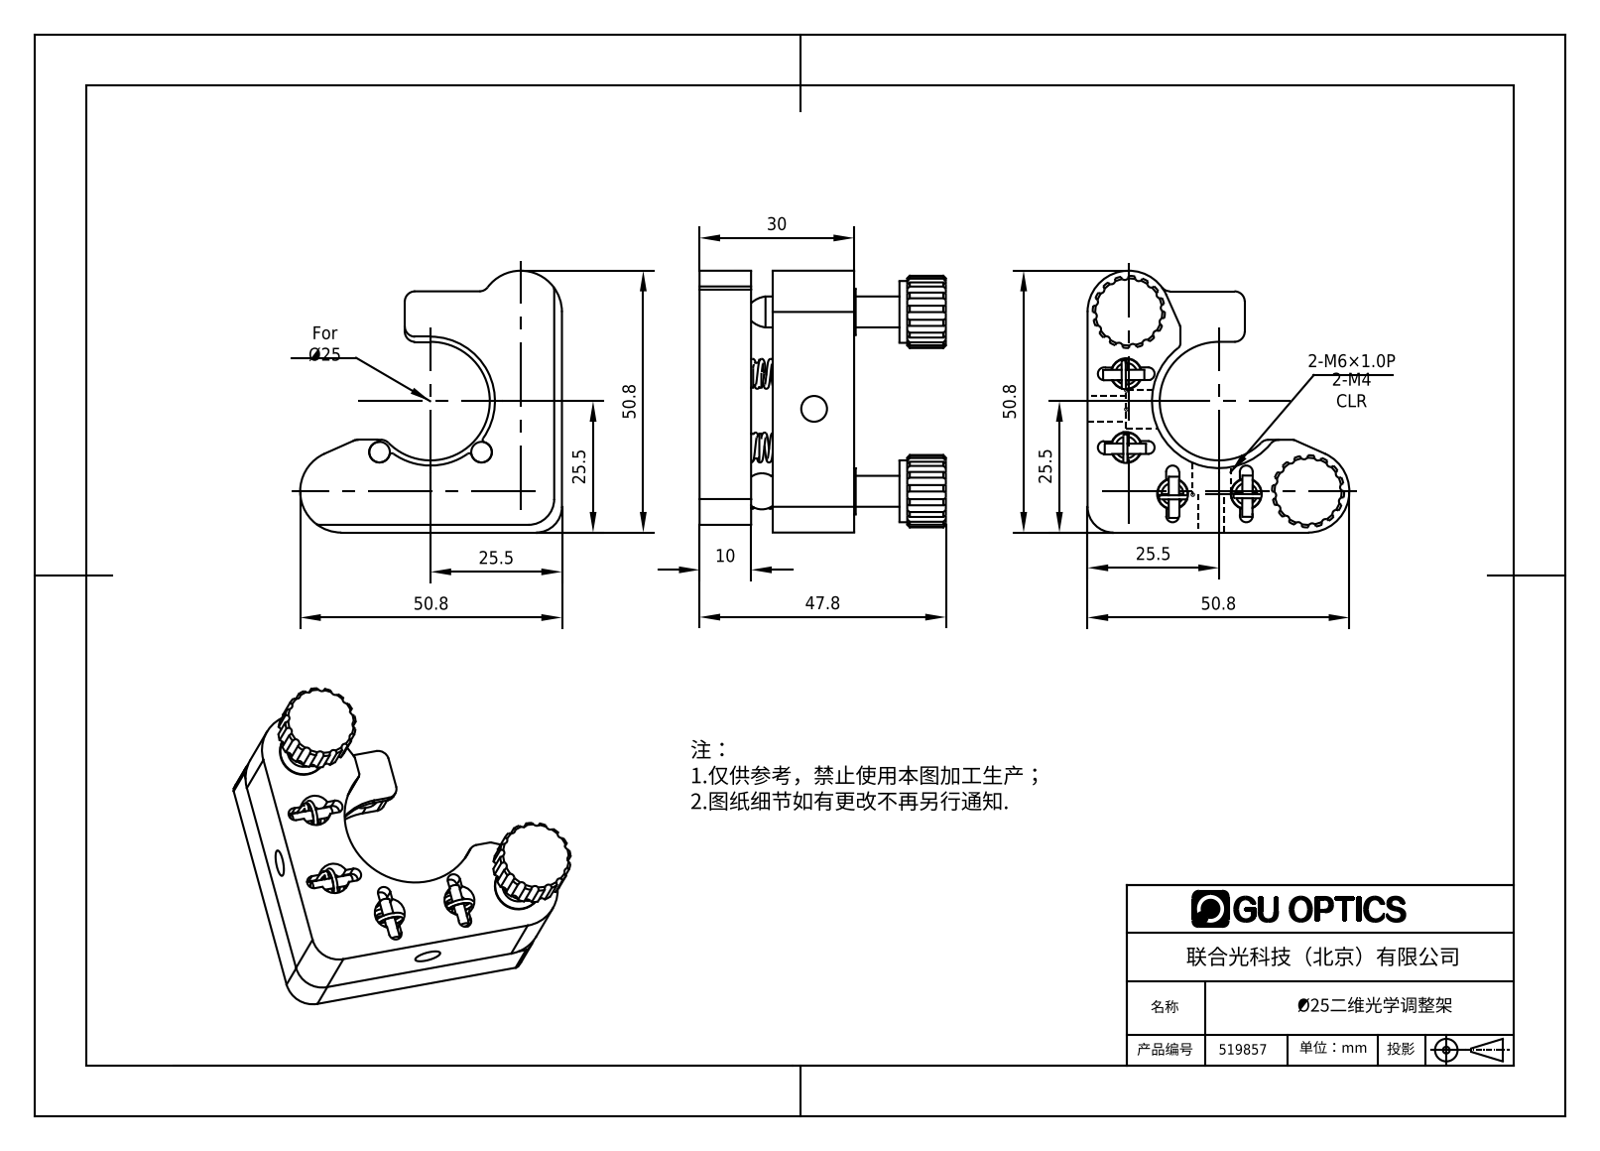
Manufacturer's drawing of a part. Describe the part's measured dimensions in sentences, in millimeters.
The part is named "519857". Its 3-D file was written by "SolidWorks 2016 (AUTOMOTIVE_DESIGN)". It is 0 solids with 617 faces: 172 planar, 218 cylindrical and 227 other. Overall it measures 65.41 by 61.31 by 54 millimeters. Round holes: 9 of diameter 6, 4 of diameter 8, 2 of diameter 5, 2 of diameter 7.5, 1 of diameter 3.5, 1 of diameter 4. Round bosses or shafts: 4 of diameter 5.4, 4 of diameter 2, 4 of diameter 0.8, 2 of diameter 12, 2 of diameter 9, 2 of diameter 6, 1 of diameter 4. Partial cylindrical surfaces (rounded edges, fillets, slot ends): 32 of radius 0.75, 8 of radius 1.25, 7 of radius 2, 6 of radius 1, 3 of radius 0.5, 3 of radius 8, 2 of radius 5, 2 of radius 7. The main face-to-face distances are 14.2, 20, 15.81, 30.01, 4.19, 10.01, 1.5, 5, 4.51, 5.01. The hole center spacings are 12.01, 42.02, 14.3, 26.31, 28.24, 36.31, 12.02, 17.22.
